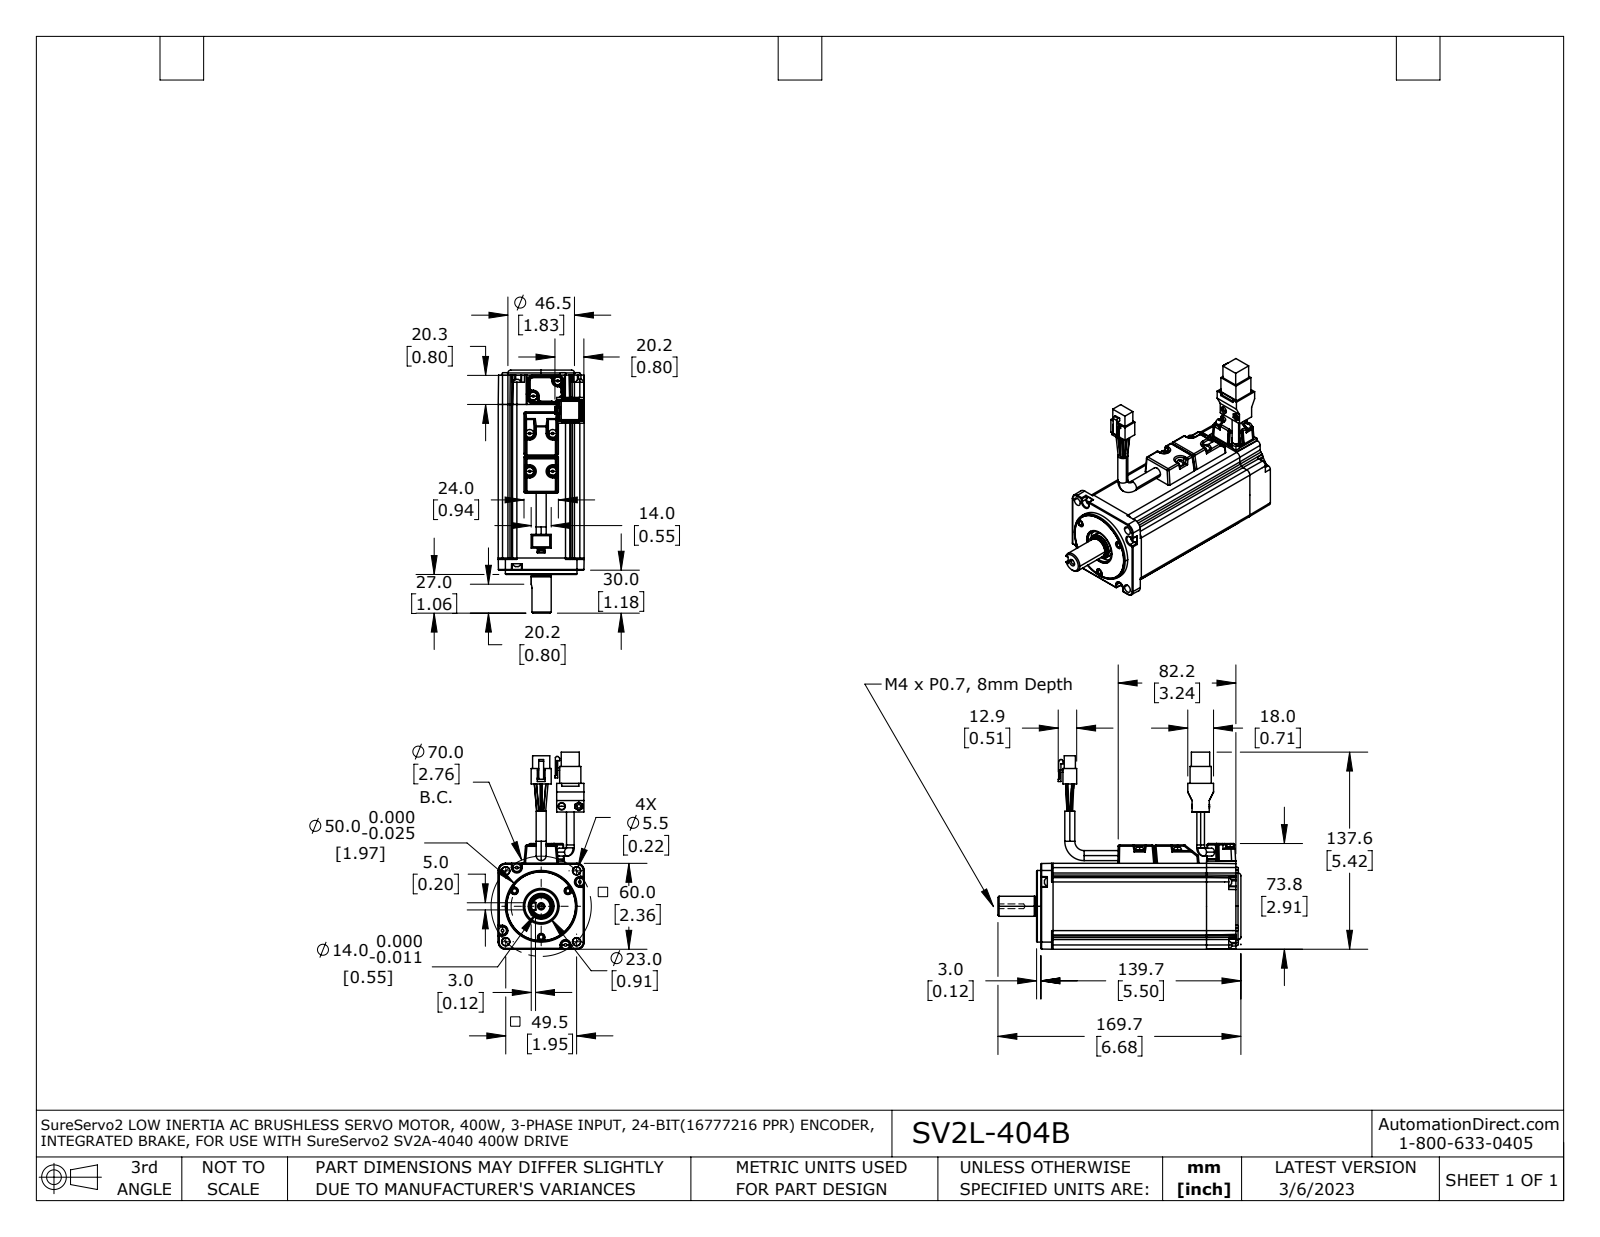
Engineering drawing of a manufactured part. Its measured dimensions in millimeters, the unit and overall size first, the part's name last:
Units: millimetres
Overall size (bounding box): 169.7 × 137.6 × 60
Round holes (diameter × count): ⌀5.1 ×2, ⌀3.3 ×1, ⌀23 ×1, ⌀25 ×1
Round bosses / shafts (diameter × count): ⌀5.5 ×8, ⌀1.5 ×6, ⌀7 ×2, ⌀4.6 ×2, ⌀4.3 ×2, ⌀3.6 ×2, ⌀2.5 ×2, ⌀50 ×1
Partial cylindrical surfaces — rounded edges, fillets, slot ends (radius × count): R1 ×52, R2 ×28, R0.5 ×24, R3 ×16, R0.8 ×4, R2.2 ×3, R2.2 ×3, R2.5 ×3
Main face-to-face distances: 60, 10, 50, 40, 3, 142.7, 3.5, 139.2, 139.7, 136.2
Hole centre spacings: 12, 71.3, 74.6
Volume: 486 900 mm³ · Surface area: 52 820 mm²
Bodies: 6 solids, 802 faces (324 planar, 261 cylindrical, 217 other)
Part name (STEP PRODUCT): SV2L-x04B ext2B coord fxt r1eb
STEP written by: SolidWorks 2021 (AUTOMOTIVE_DESIGN)
